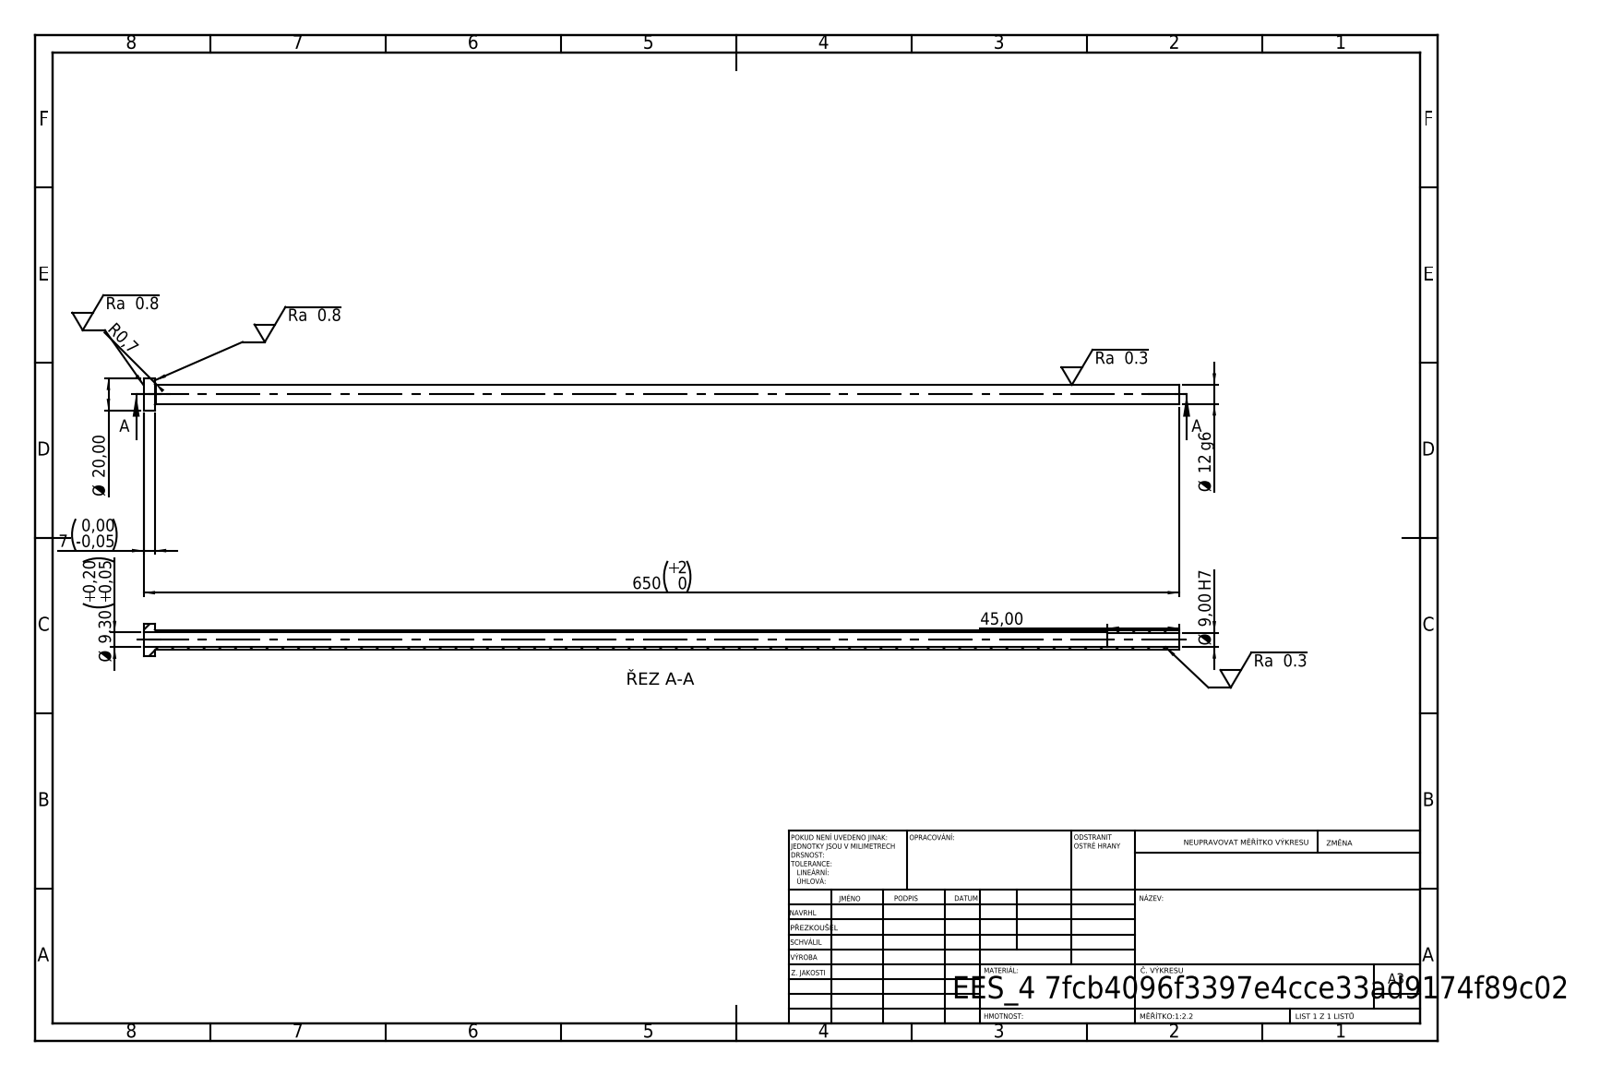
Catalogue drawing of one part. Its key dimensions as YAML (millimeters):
step_written_by: "SolidWorks 2019 (CONFIG_CONTROL_DESIGN)"
units: millimeters
bodies: {solids: 1, faces: 14, planar: 4, cylindrical: 8, other: 2}
overall_size: [650, 20, 20]
volume: 30965
surface_area: 44119
round_holes:
  - {diameter: 9, count: 1}
  - {diameter: 9.3, count: 1}
round_bosses_or_shafts:
  - {diameter: 20, count: 1}
  - {diameter: 12, count: 1}
face_to_face_distances: [7, 650, 643, 605, 598, 45]
